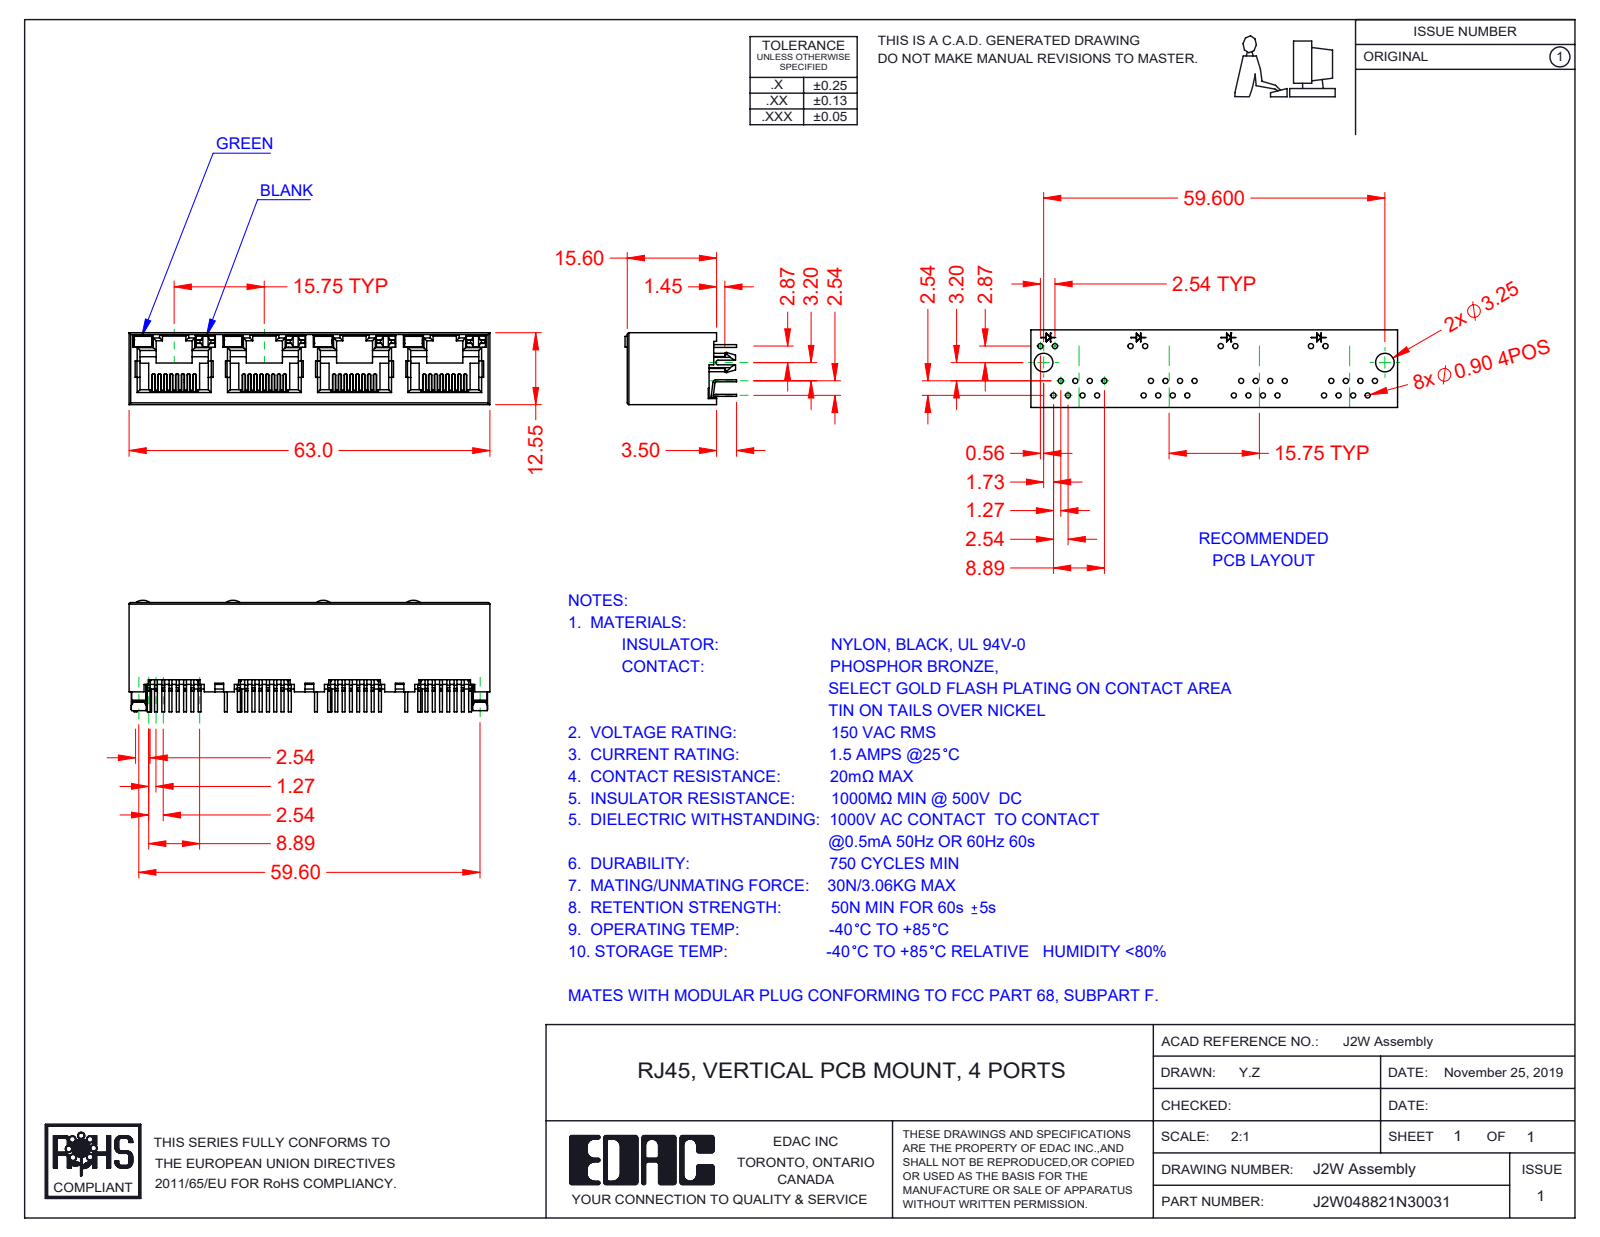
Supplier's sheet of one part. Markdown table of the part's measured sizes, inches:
| quantity | value |
| --- | --- |
| part name | J2W048821N30031; 2W LED RH_0-Blank; 2W LED LH_3-Green; 2W Insulator (+2 more) |
| STEP written by | SolidWorks 2020 (CONFIG_CONTROL_DESIGN) |
| units | inches |
| bodies | 41 solids, 3007 faces (2508 planar, 441 cylindrical, 58 other) |
| overall size | 2.48 × 0.768 × 0.494 |
| volume | 0.318 in³ |
| surface area | 19.68 in² |
| partial cylindrical surfaces (radius × count) | 0.006 × 64, 0.008 × 29, 0.02 × 28, 0.012 × 14, 0.018 × 8, 0.079 × 4, 0.01 × 2, 0.059 × 2 |
| main face-to-face distances | 0.494, 0.469, 0.026, 0.62, 0.014, 0.059, 0.031, 0.024, 0.445, 1.24 |
